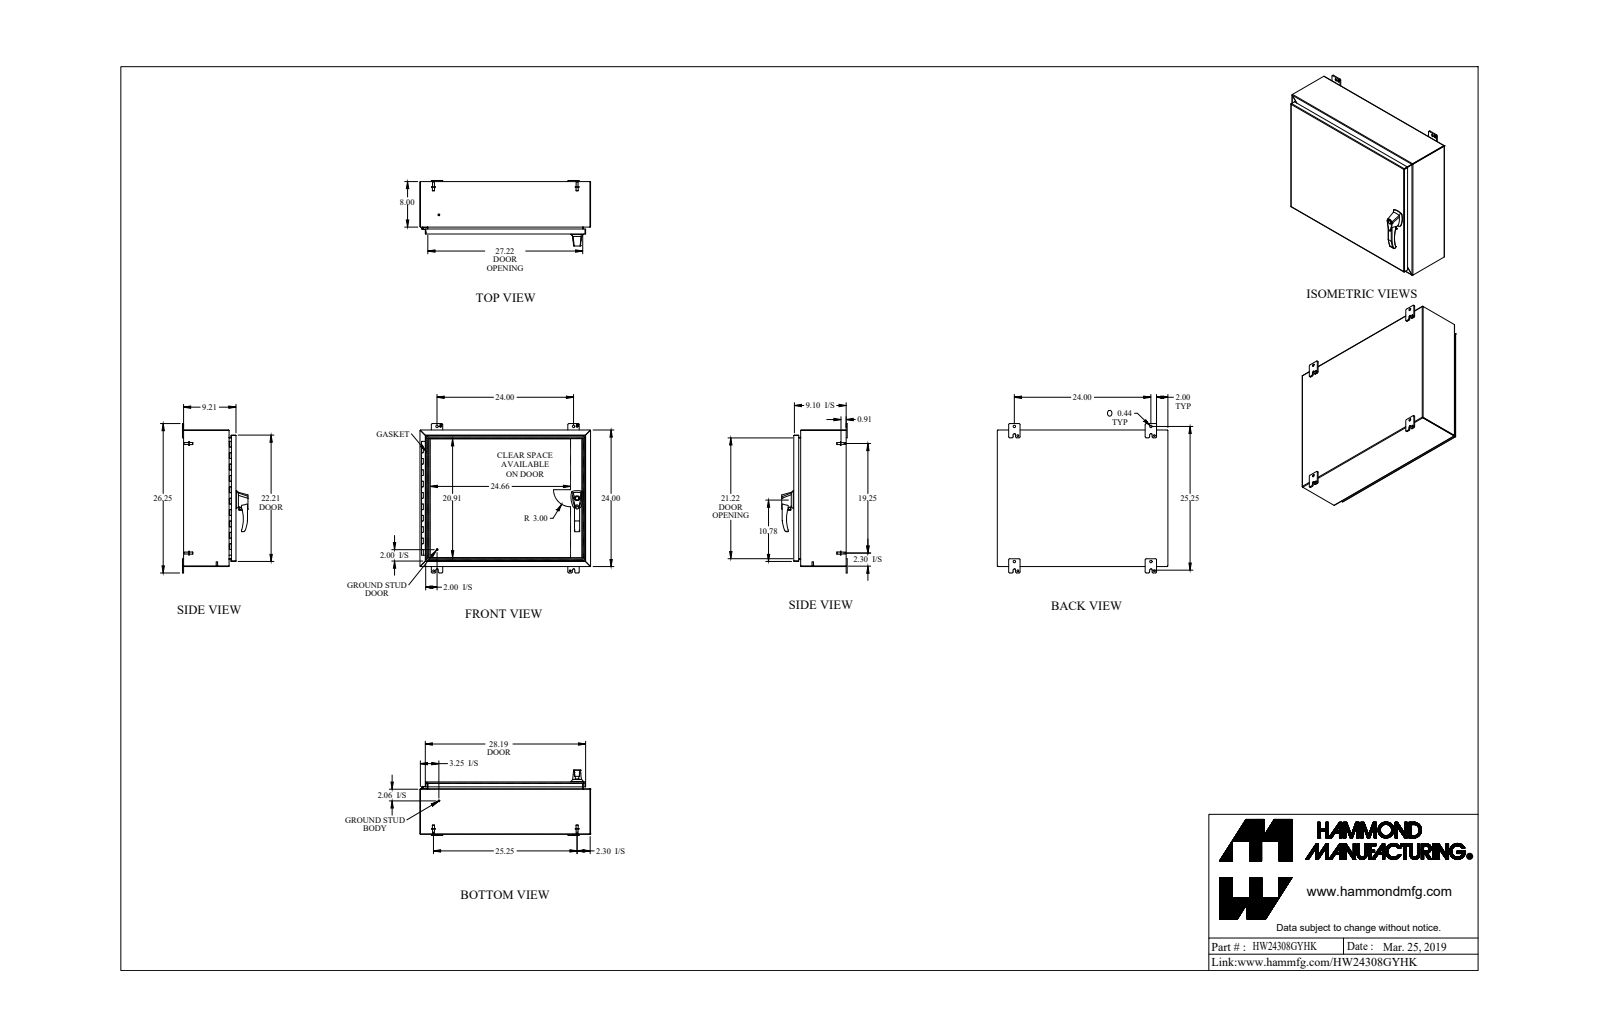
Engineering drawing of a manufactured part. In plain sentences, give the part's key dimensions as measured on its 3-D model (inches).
The part is named "HW24308GYHK". Its 3-D file was written by "SolidWorks 2018 (AUTOMOTIVE_DESIGN)". It is 53 solids with 1498 faces: 760 planar, 554 cylindrical and 184 other. Overall it measures 30 by 26.25 by 11.512 inches. Its volume is 219.2 cubic inches and its surface area 5 589 square inches. Round holes: 6 of diameter 0.173, 4 of diameter 0.25, 4 of diameter 0.307, 4 of diameter 0.313, 4 of diameter 0.445, 3 of diameter 0.196, 3 of diameter 0.265, 2 of diameter 0.256, 2 of diameter 0.394, 2 of diameter 0.437, 1 of diameter 0.187, 1 of diameter 0.233. Round bosses or shafts: 9 of diameter 0.375, 7 of diameter 1, 6 of diameter 0.25, 6 of diameter 0.156, 4 of diameter 0.65, 4 of diameter 0.33, 2 of diameter 0.63, 2 of diameter 0.51. Partial cylindrical surfaces (rounded edges, fillets, slot ends): 30 of radius 0.25, 20 of radius 0.188, 12 of radius 0.048, 12 of radius 0.06, 12 of radius 0.12, 8 of radius 0.036, 8 of radius 0.045, 8 of radius 0.108. The main face-to-face distances are 0.072, 0.072, 9.138, 9.066, 9.21, 9.138, 23.928, 29.928, 7.928, 23.856. The hole center spacings are 30.859, 8.118, 8.119, 16.237, 19.25, 19.25, 22.259, 25.25.
